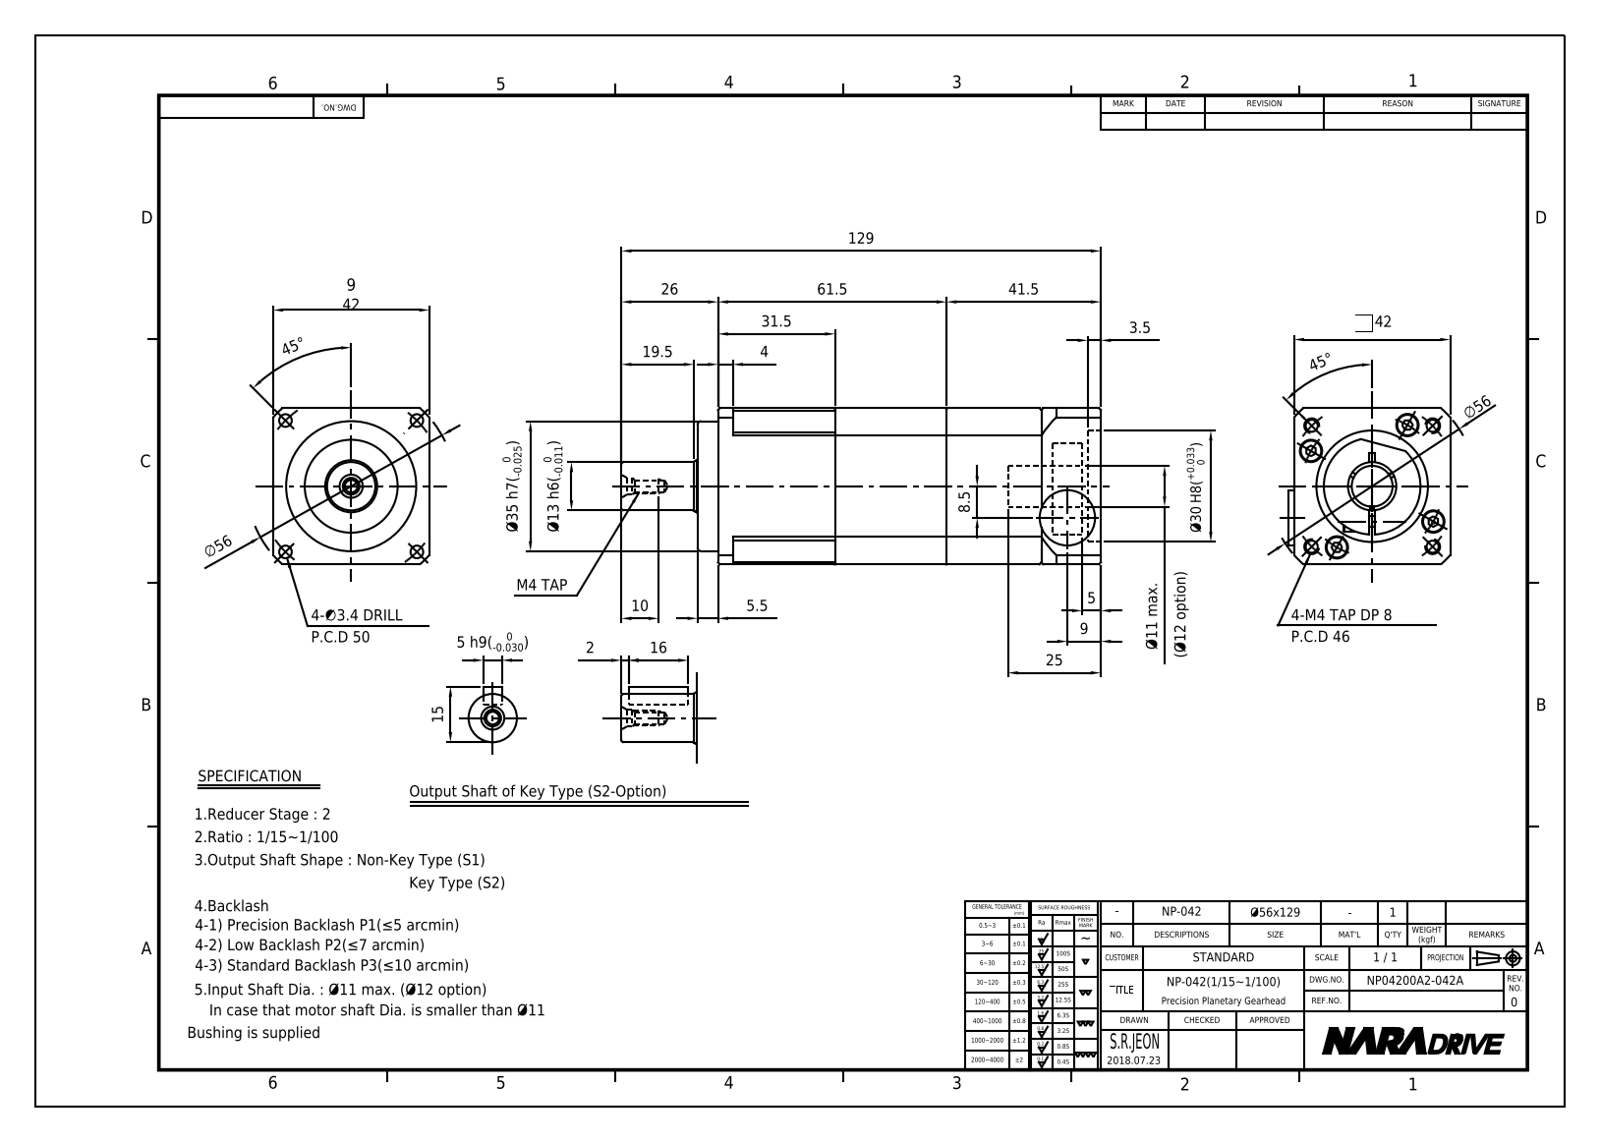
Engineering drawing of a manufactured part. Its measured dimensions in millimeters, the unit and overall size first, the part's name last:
Units: millimetres
Overall size (bounding box): 129 × 43.5 × 42
Round holes (diameter × count): ⌀3.4 ×13, ⌀2.46 ×9, ⌀6 ×8, ⌀3.24 ×5, ⌀4.5 ×1, ⌀7 ×1, ⌀8.5 ×1, ⌀11 ×1, ⌀13 ×1, ⌀27 ×1, ⌀28 ×1, ⌀30 ×1
Round bosses / shafts (diameter × count): ⌀5.5 ×5, ⌀3 ×5, ⌀35 ×1, ⌀26 ×1, ⌀25 ×1, ⌀15 ×1, ⌀14 ×1, ⌀8 ×1
Partial cylindrical surfaces — rounded edges, fillets, slot ends (radius × count): R5 ×4, R3 ×1, R25 ×1, R28 ×1
Main face-to-face distances: 42, 25.5, 103, 77.5, 5.5, 31, 108.5, 5, 8, 103.5
Hole centre spacings: 5.44, 8.27, 19, 25, 27.21, 27.29, 29.34, 32.53
Volume: 125 556 mm³ · Surface area: 37 490 mm²
Bodies: 2 solids, 325 faces (158 planar, 86 cylindrical, 81 other)
Part name (STEP PRODUCT): NP04200A2-042A-S1
STEP written by: Autodesk Inventor 2015 (AUTOMOTIVE_DESIGN)
